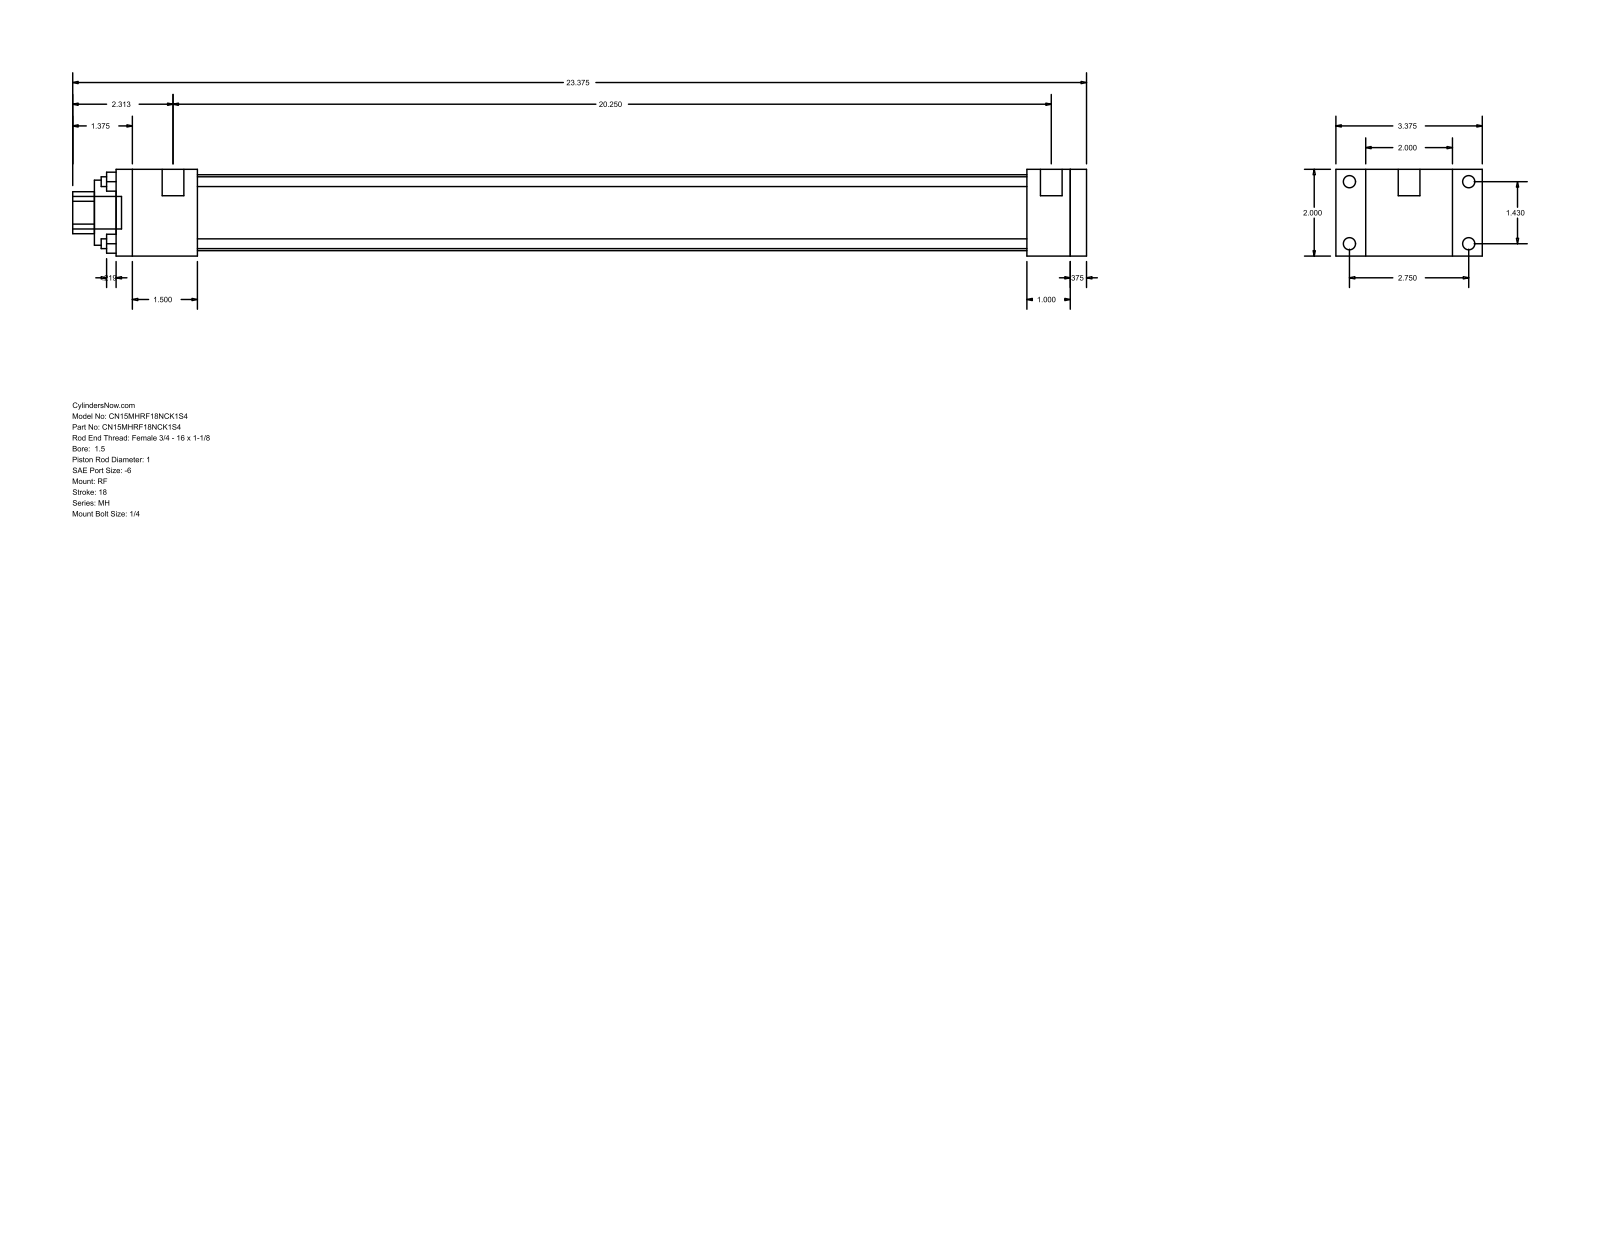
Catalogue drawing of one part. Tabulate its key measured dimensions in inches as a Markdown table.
| quantity | value |
| --- | --- |
| part name | MH_RF__0150_1 |
| STEP written by | GSSL Pune (CONFIG_CONTROL_DESIGN) |
| units | inches |
| bodies | 0 solids, 92 faces (64 planar, 28 cylindrical, 0 other) |
| overall size | 23.375 × 3.375 × 2 |
| round holes (diameter × count) | 0.225 × 4, 1 × 1, 1.5 × 1, 1.75 × 1 |
| round bosses / shafts (diameter × count) | 0.281 × 4, 0.219 × 4, 0.5 × 2, 0.75 × 1 |
| partial cylindrical surfaces (radius × count) | 0.484 × 1 |
| main face-to-face distances | 2, 0.375, 22, 1, 22.375, 0.687, 2.687, 21, 1.375, 1.875 |
| hole center spacings | 1.011, 1.43, 2.022 |
